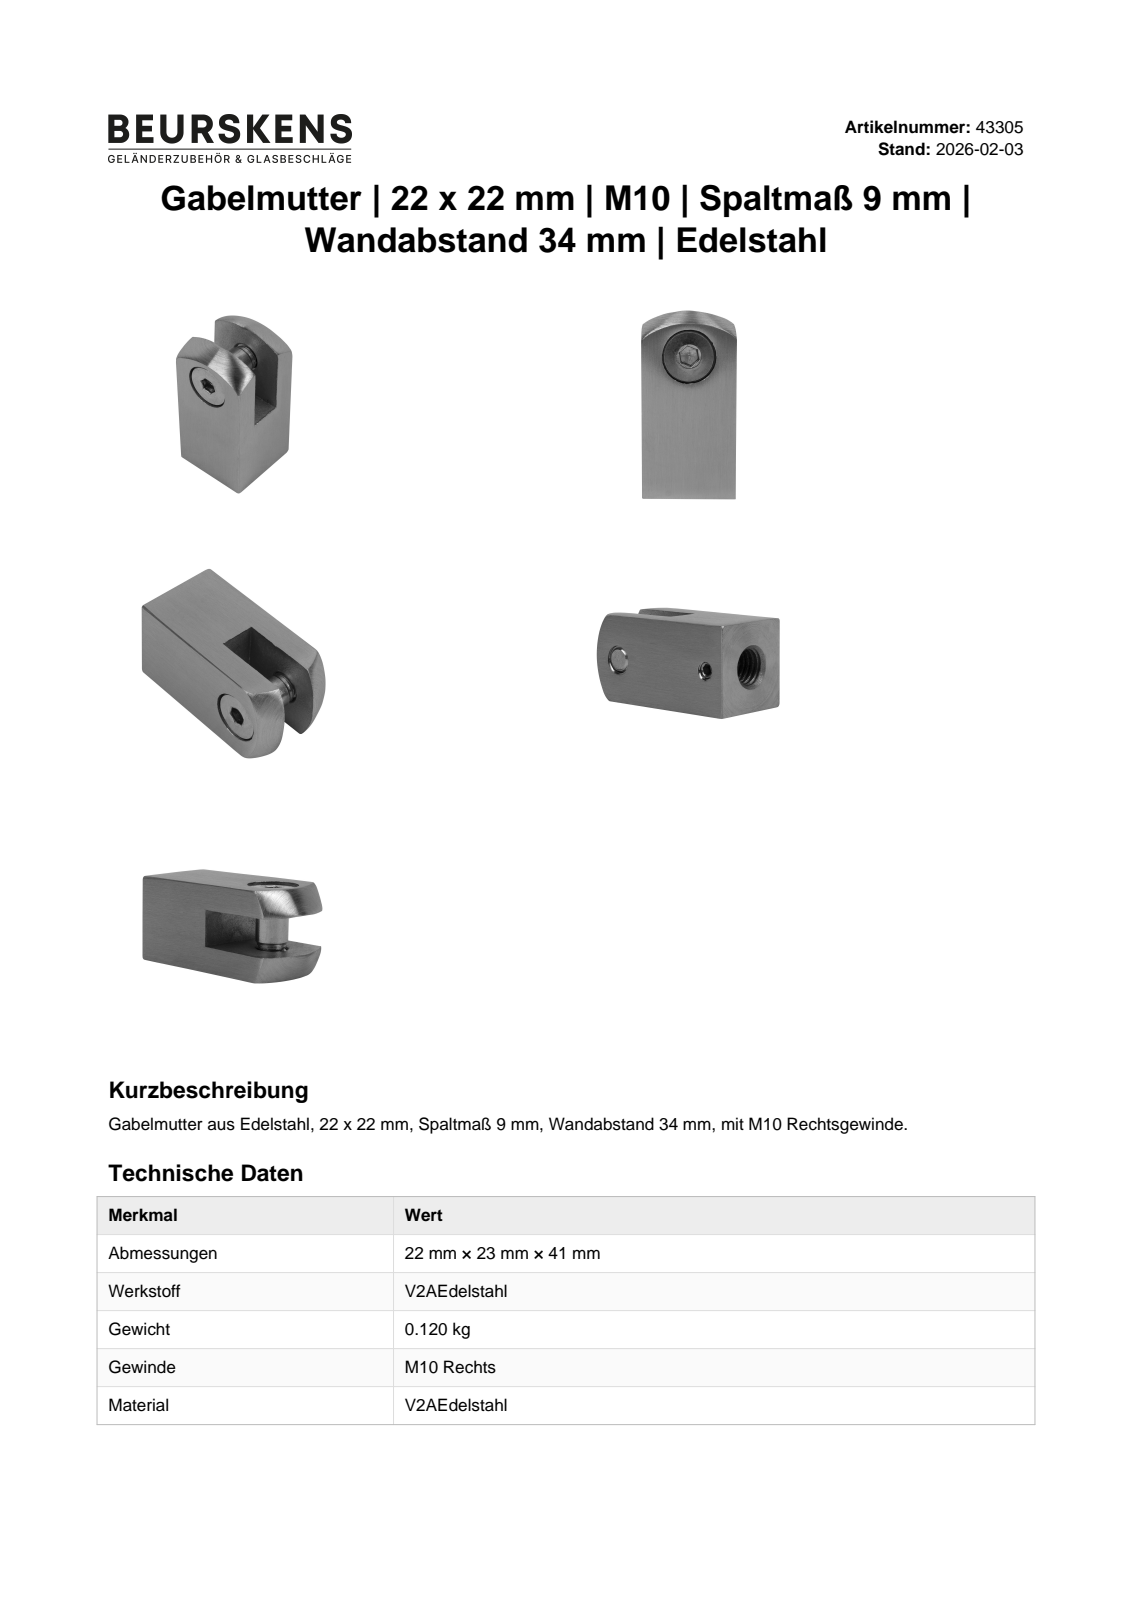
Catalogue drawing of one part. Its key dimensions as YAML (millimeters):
part_name: "43305; 43305 Einzelteil; M8 Schraube für Gabelmuttern; DIN 914 - M5 x 6"
step_written_by: "Autodesk Inventor 2022 (AUTOMOTIVE_DESIGN)"
units: millimeters
bodies: {solids: 3, faces: 42, planar: 27, cylindrical: 8, other: 7}
overall_size: [43.99, 22, 22]
volume: 15247
surface_area: 6693
round_holes:
  - {diameter: 5, count: 1}
  - {diameter: 8, count: 1}
  - {diameter: 10, count: 1}
  - {diameter: 12.5, count: 1}
round_bosses_or_shafts:
  - {diameter: 12, count: 1}
face_to_face_distances: [22, 15.5, 6.5, 9, 1, 19.5, 18.5, 20.5, 14, 5]
hole_center_spacings: [29]
